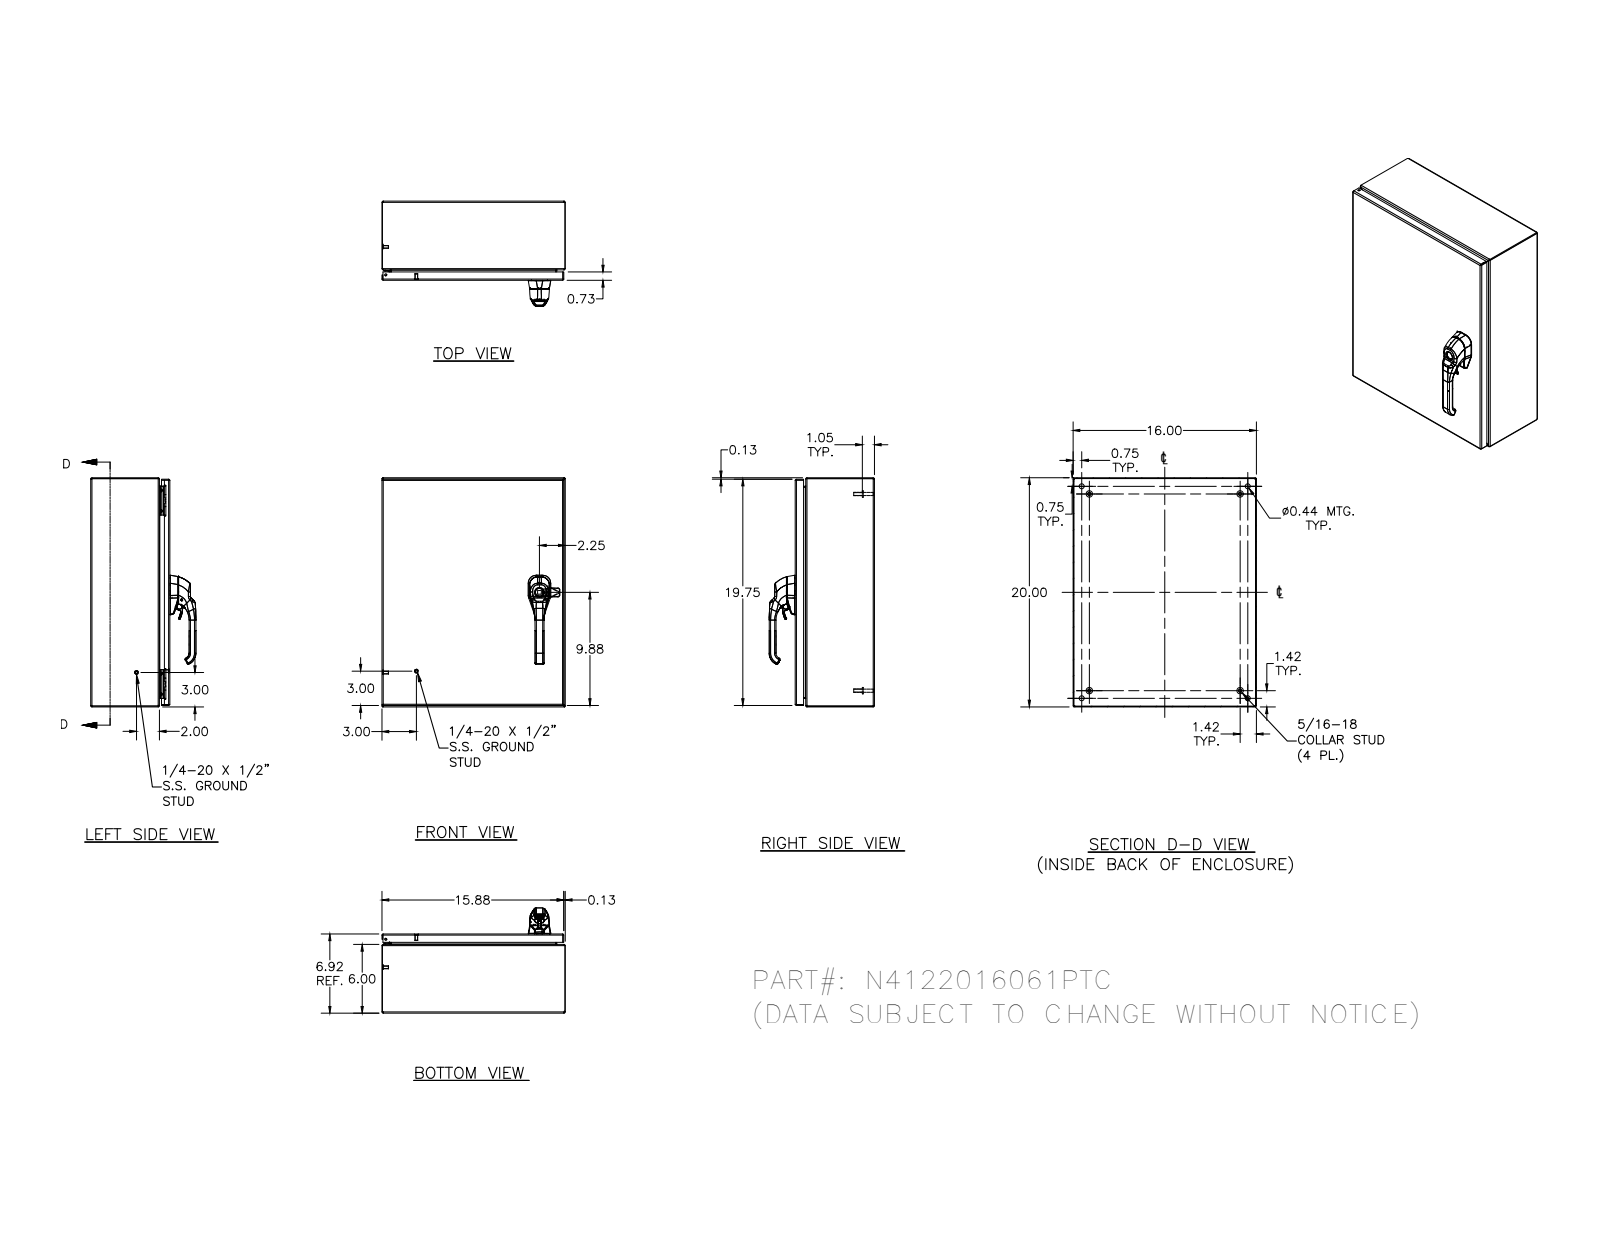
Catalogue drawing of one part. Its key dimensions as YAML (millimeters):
part_name: "N4122016061PTC"
step_written_by: "SolidWorks 2018 (AUTOMOTIVE_DESIGN)"
units: millimeters
bodies: {solids: 28, faces: 1280, planar: 417, cylindrical: 474, other: 389}
overall_size: [508, 406.4, 231]
volume: 1635000
surface_area: 1606000
round_holes:
  - {diameter: 4.8, count: 5}
  - {diameter: 2.4, count: 4}
  - {diameter: 3.9, count: 4}
  - {diameter: 4.2, count: 4}
  - {diameter: 4.4, count: 4}
  - {diameter: 11.1, count: 4}
  - {diameter: 7.1, count: 3}
  - {diameter: 4, count: 2}
  - {diameter: 4.7, count: 1}
round_bosses_or_shafts:
  - {diameter: 6.4, count: 10}
  - {diameter: 14.3, count: 4}
  - {diameter: 9.1, count: 4}
  - {diameter: 8.1, count: 4}
  - {diameter: 7.6, count: 4}
  - {diameter: 7, count: 4}
  - {diameter: 6.5, count: 4}
  - {diameter: 4.2, count: 4}
partial_cylinders:
  - {radius: 0.8, count: 30}
  - {radius: 1.3, count: 26}
  - {radius: 2.7, count: 20}
  - {radius: 0.4, count: 18}
  - {radius: 3.2, count: 14}
  - {radius: 0.8, count: 8}
  - {radius: 1.7, count: 8}
  - {radius: 1.7, count: 8}
face_to_face_distances: [1.9, 173.8, 175.7, 171.9, 404.5, 506.1, 402.6, 406.4, 508, 504.2]
hole_center_spacings: [406.3, 0.4, 16.8, 406.5, 423.1, 0.5, 12.7, 16.5]
